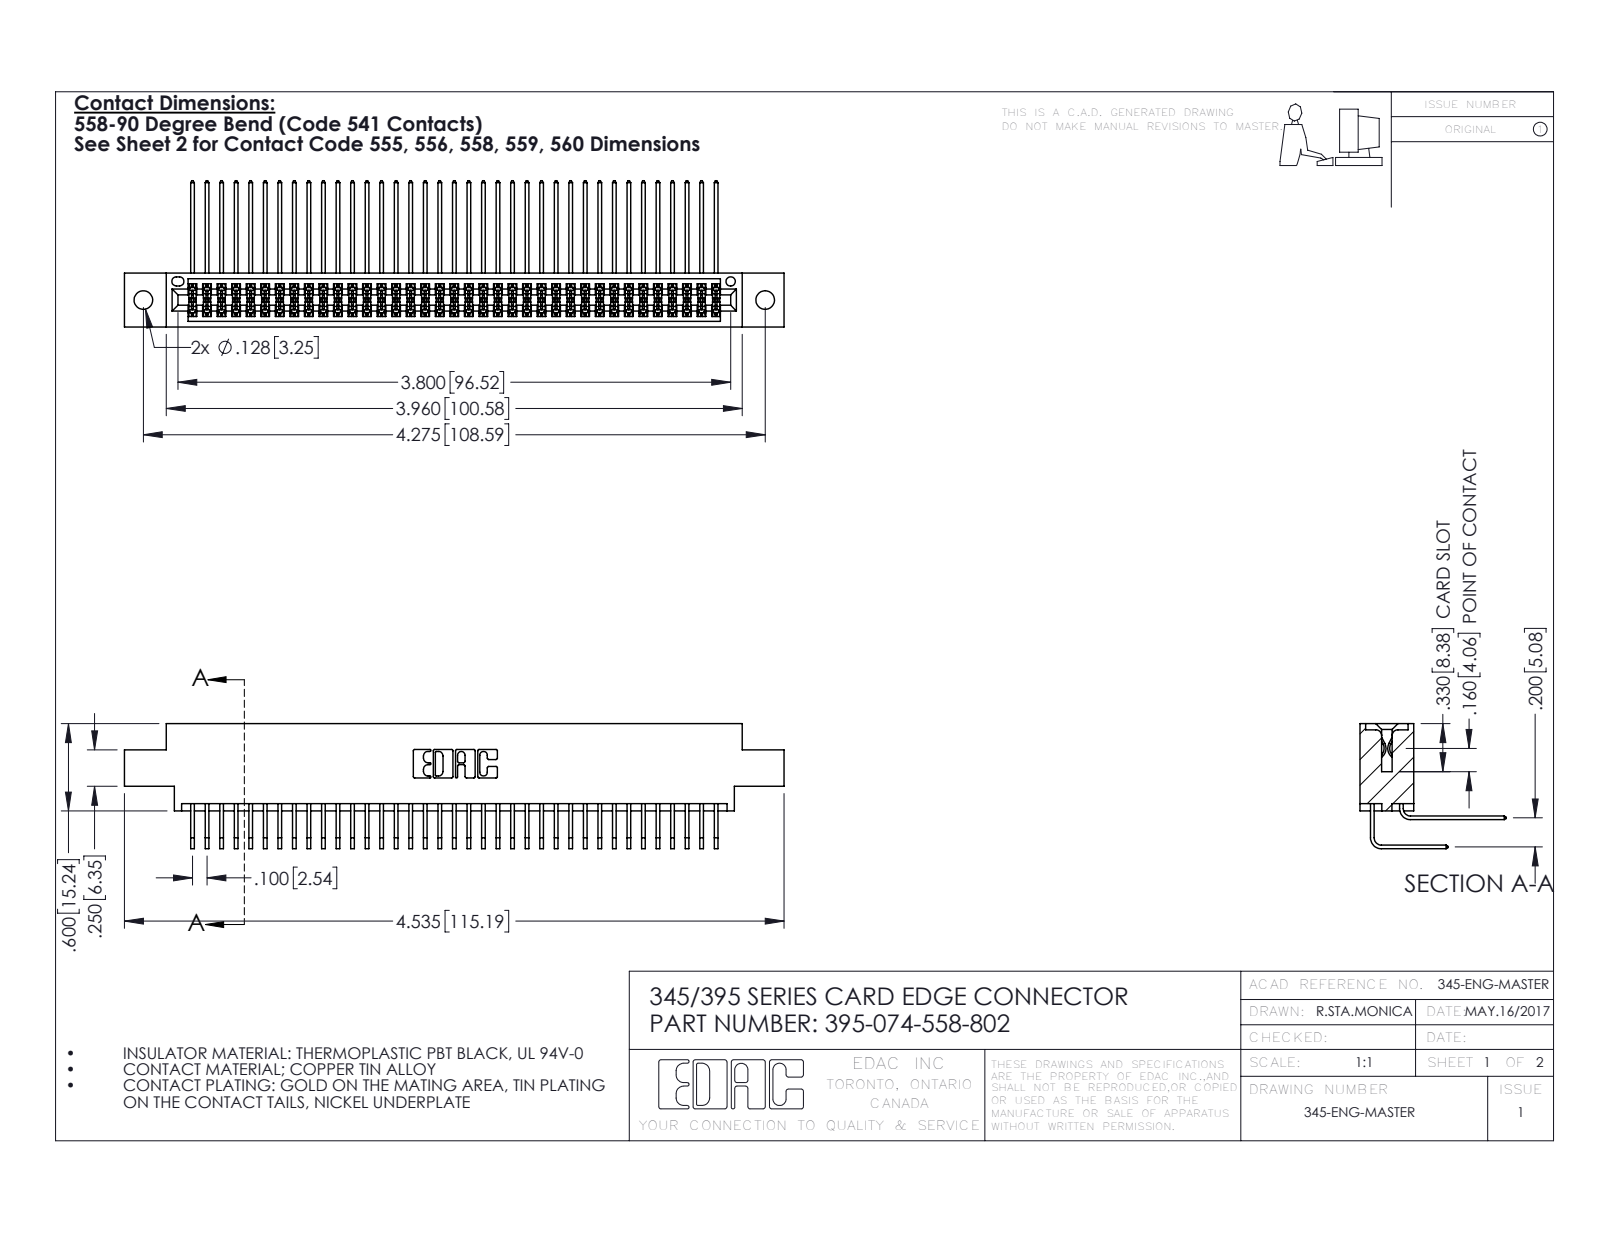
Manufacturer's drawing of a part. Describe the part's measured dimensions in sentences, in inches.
The part is named "345-292-001_558 559 Tail - 1; 345-292-001_558 Tail - 2; 395-074-558-802; 345 Part_0.170 Offset - 0.128 Dia". Its 3-D file was written by "SolidWorks 2016 (CONFIG_CONTROL_DESIGN)". It is 75 solids with 3978 faces: 2674 planar, 1304 cylindrical and 0 other. Overall it measures 4.535 by 1.005 by 0.859 inches. Its volume is 0.697 cubic inches and its surface area 28.93 square inches. Round holes: 2 of diameter 0.128, 1 of diameter 0.064. Partial cylindrical surfaces (rounded edges, fillets, slot ends): 112 of radius 0.006, 22 of radius 0.01, 6 of radius 0.007, 6 of radius 0.031, 3 of radius 0.026, 2 of radius 0.014, 2 of radius 0.019, 2 of radius 0.022. The main face-to-face distances are 0.072, 0.298, 0.2, 0.37, 0.098, 0.272, 0.025, 0.225, 0.175, 0.025. The hole center spacings are 0.27, 4.039, 4.275.
